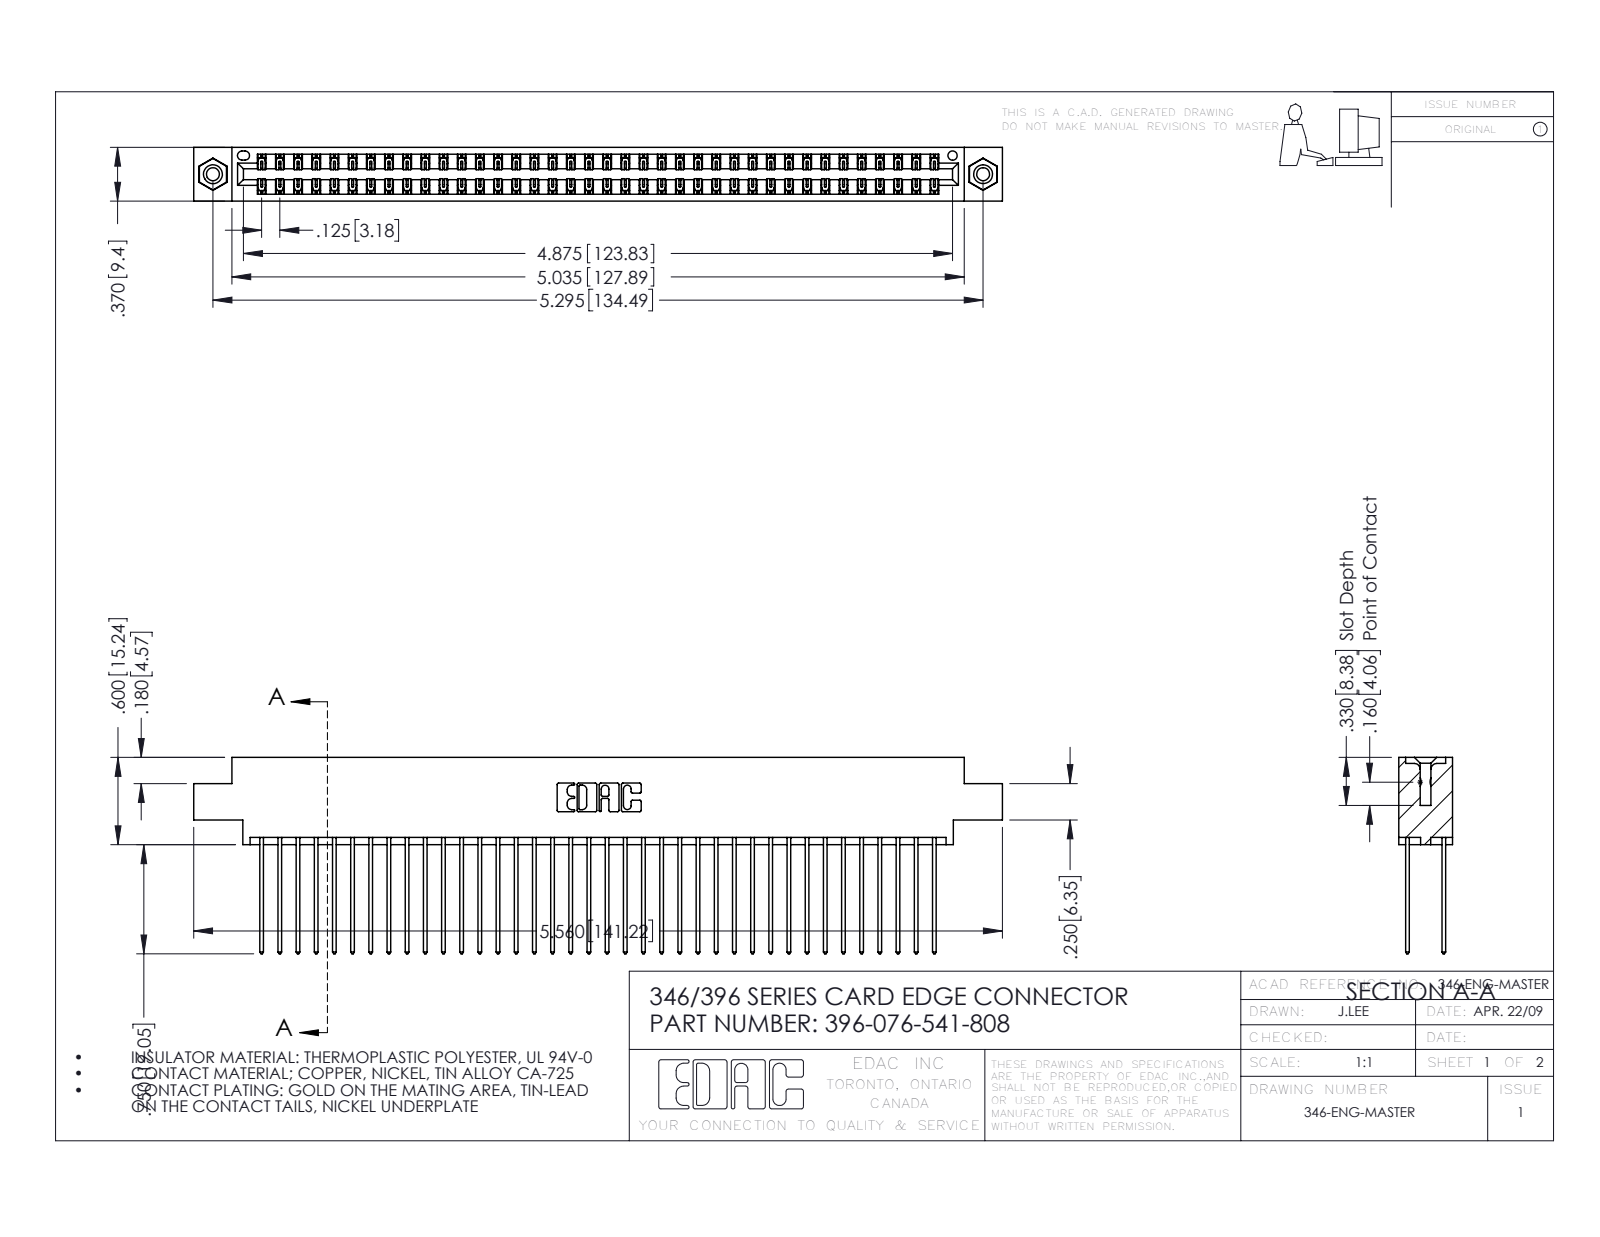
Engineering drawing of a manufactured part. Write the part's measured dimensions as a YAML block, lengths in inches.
part_name: "346 Part_0.170 Offset - 0.156 Dia-TI; 345-292-001_345-293-141; 345-250-001_345-250-003-102; 396-076-541-808"
step_written_by: "SolidWorks 2016 (CONFIG_CONTROL_DESIGN)"
units: inches
bodies: {solids: 79, faces: 4138, planar: 2772, cylindrical: 1350, other: 16}
overall_size: [5.56, 1.35, 0.37]
volume: 0.855
surface_area: 33.31
round_holes:
  - {diameter: 0.089, count: 2}
  - {diameter: 0.125, count: 2}
  - {diameter: 0.156, count: 2}
  - {diameter: 0.064, count: 1}
round_bosses_or_shafts:
  - {diameter: 0.155, count: 2}
partial_cylinders:
  - {radius: 0.006, count: 114}
  - {radius: 0.01, count: 76}
  - {radius: 0.01, count: 22}
  - {radius: 0.007, count: 6}
  - {radius: 0.031, count: 6}
  - {radius: 0.026, count: 3}
  - {radius: 0.014, count: 2}
  - {radius: 0.022, count: 2}
face_to_face_distances: [0.048, 0.322, 0.25, 0.072, 0.298, 0.025, 0.37, 0.275, 0.222, 0.225]
hole_center_spacings: [0.246, 5.086, 5.295]
